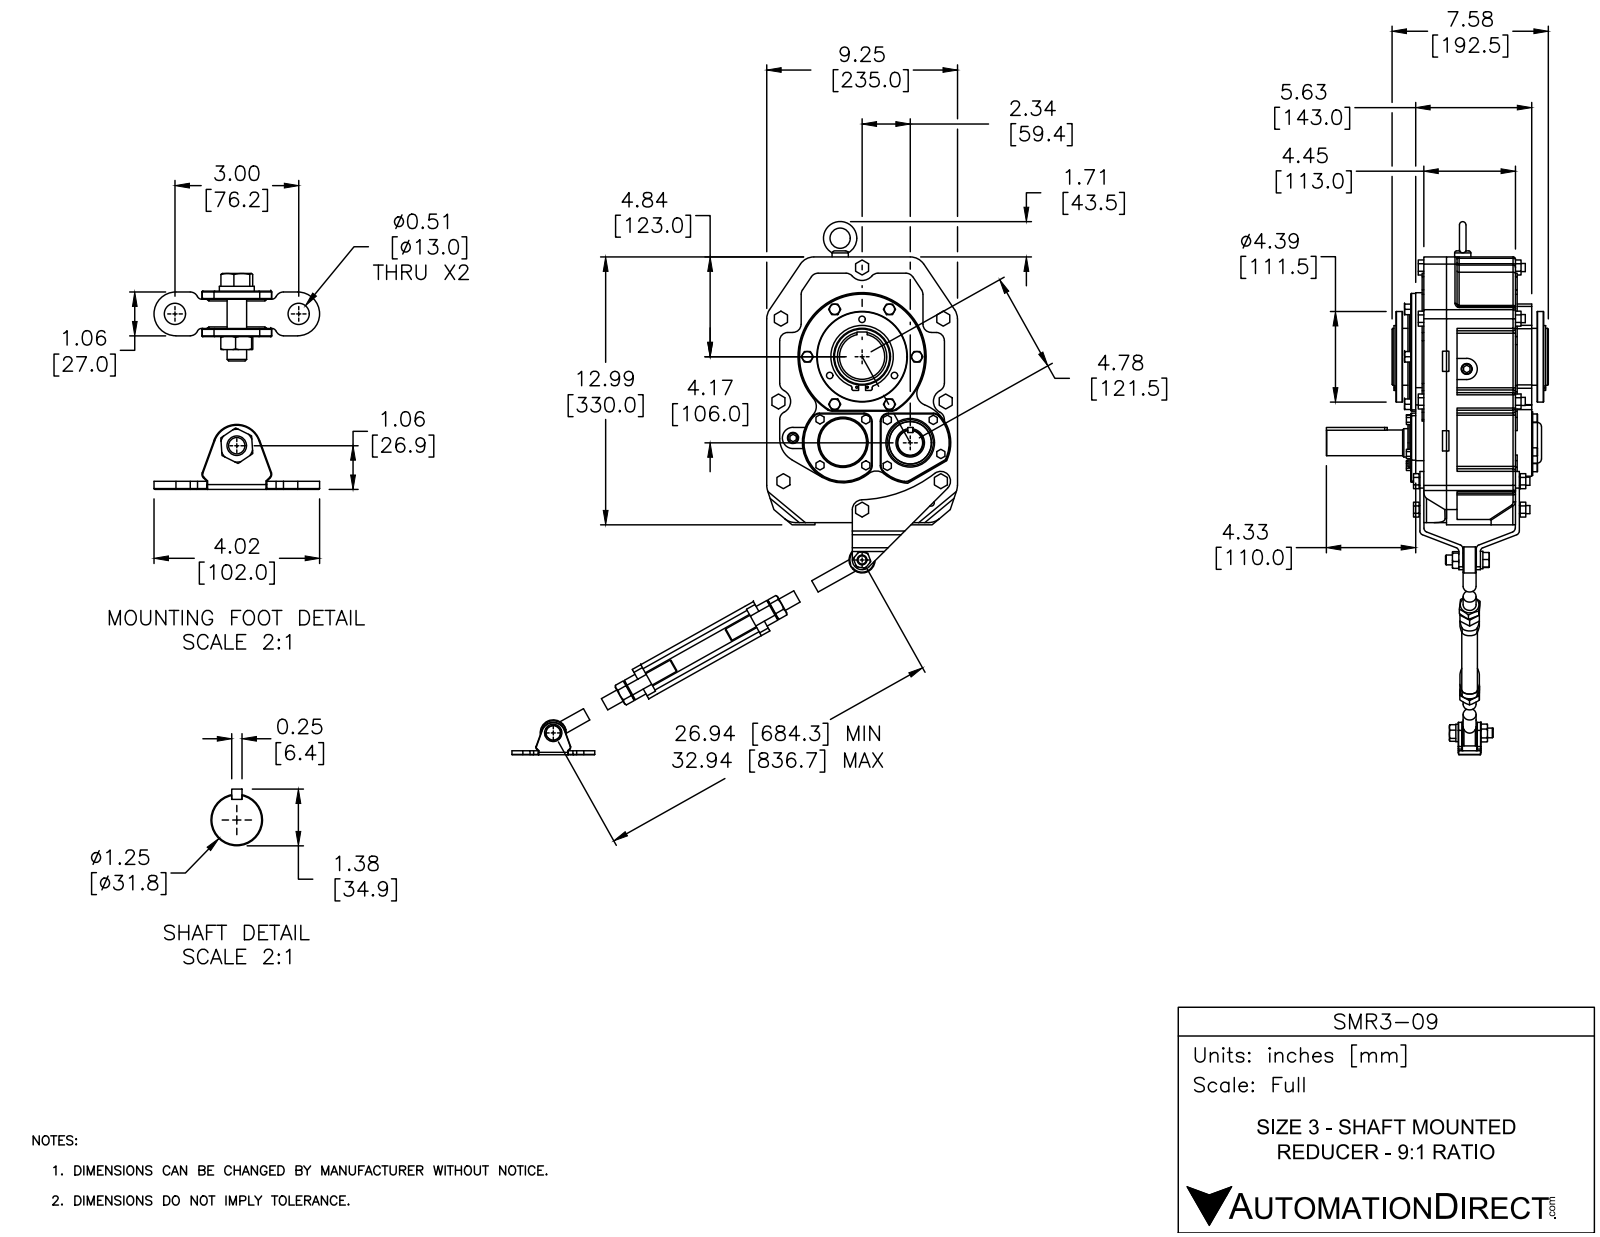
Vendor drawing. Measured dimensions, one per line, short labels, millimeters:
name: SMR3-TA_5; SMR3-TA_4; SMR3-TA_3; SMR3-TA_2 (+4 more)
written by: SolidWorks 2016 (AUTOMOTIVE_DESIGN)
unit: mm
bodies: 71 solids, 1559 faces (727 planar, 556 cylindrical, 276 other)
size: 860.9 × 831.4 × 273.5
volume: 8 860 000 mm³; area: 916 800 mm²
holes: 8× ⌀10, 8× ⌀11, 7× ⌀8, 5× ⌀13, 4× ⌀12.7, 2× ⌀2.5, 2× ⌀12, 2× ⌀12.2, 2× ⌀12.9, 2× ⌀13.3, 2× ⌀16, 1× ⌀8
bosses: 5× ⌀13, 4× ⌀10, 2× ⌀60, 2× ⌀50, 2× ⌀32, 2× ⌀22.3, 2× ⌀21.5, 2× ⌀16
rounds: 80× R3, 35× R10, 22× R0.5, 16× R5, 12× R2.5, 10× R20, 9× R15, 7× R1
face distances: 10, 38, 115, 2, 28, 143, 133, 105, 8, 18
hole spacings: 70, 99, 46.1, 79.7, 28.2, 36.4, 38, 44.6
